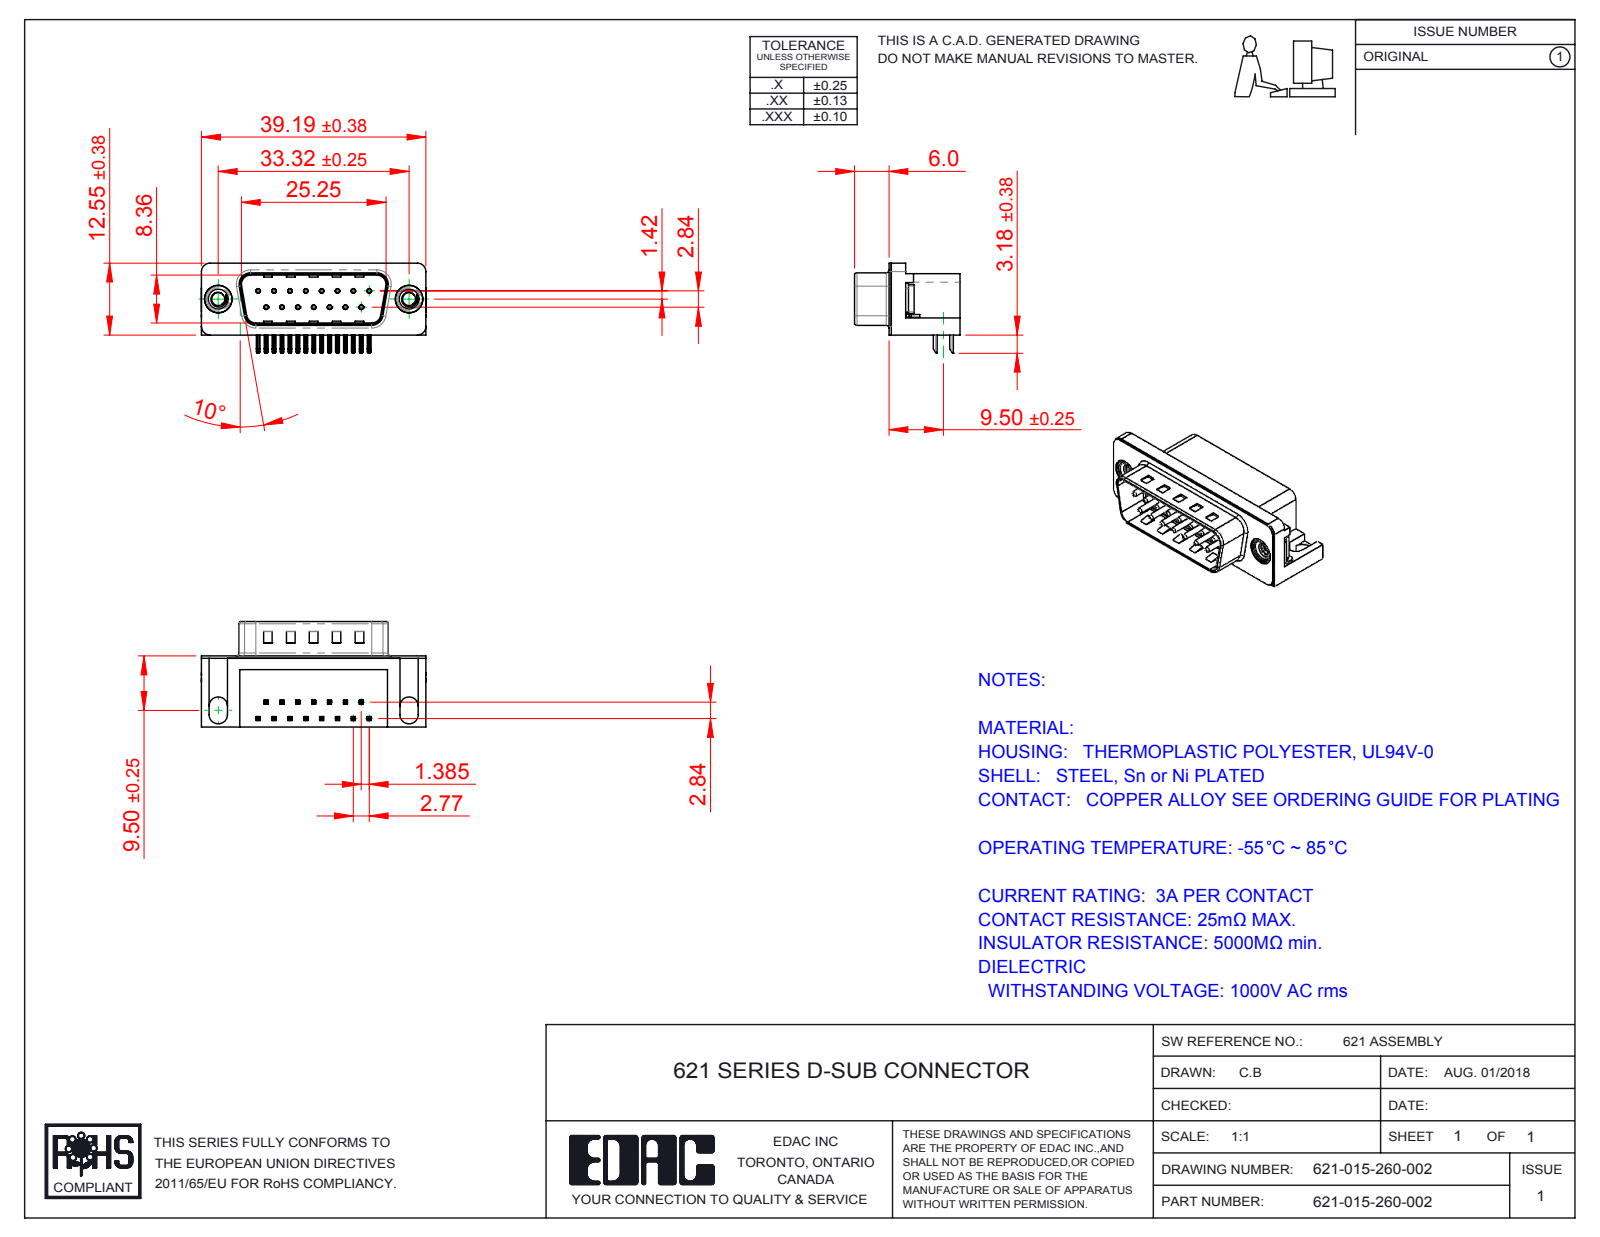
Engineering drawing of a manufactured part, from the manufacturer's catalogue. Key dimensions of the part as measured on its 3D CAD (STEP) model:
Part name (STEP PRODUCT): 621 Housing_15 Socket; 621-015-260-002; 621 Non Board Mount; 621 Contact Top (+3 more)
STEP written by: SolidWorks 2016 (CONFIG_CONTROL_DESIGN)
Units: millimetres
Bodies: 21 solids, 1471 faces (891 planar, 441 cylindrical, 139 other)
Overall size (bounding box): 39.22 × 18.4 × 15.73
Volume: 4 380 mm³ · Surface area: 5 478 mm²
Round holes (diameter × count): ⌀0.35 ×15, ⌀0.8 ×15, ⌀2.26 ×2, ⌀4 ×2, ⌀4.8 ×2, ⌀5 ×2
Round bosses / shafts (diameter × count): ⌀0.75 ×15, ⌀4.9 ×2, ⌀4.75 ×2, ⌀3.9 ×2
Partial cylindrical surfaces — rounded edges, fillets, slot ends (radius × count): R0.25 ×68, R0.12 ×30, R1 ×16, R0.5 ×9, R1.6 ×8, R1.5 ×6, R0.9 ×4, R2 ×4
Main face-to-face distances: 0.4, 12, 10.35, 2.1, 10.46, 12.4, 1.7, 10.86, 8.76, 2.9
Hole centre spacings: 3.16, 2.77, 5.54, 8.31, 11.08, 5.03, 5.04, 7.48
